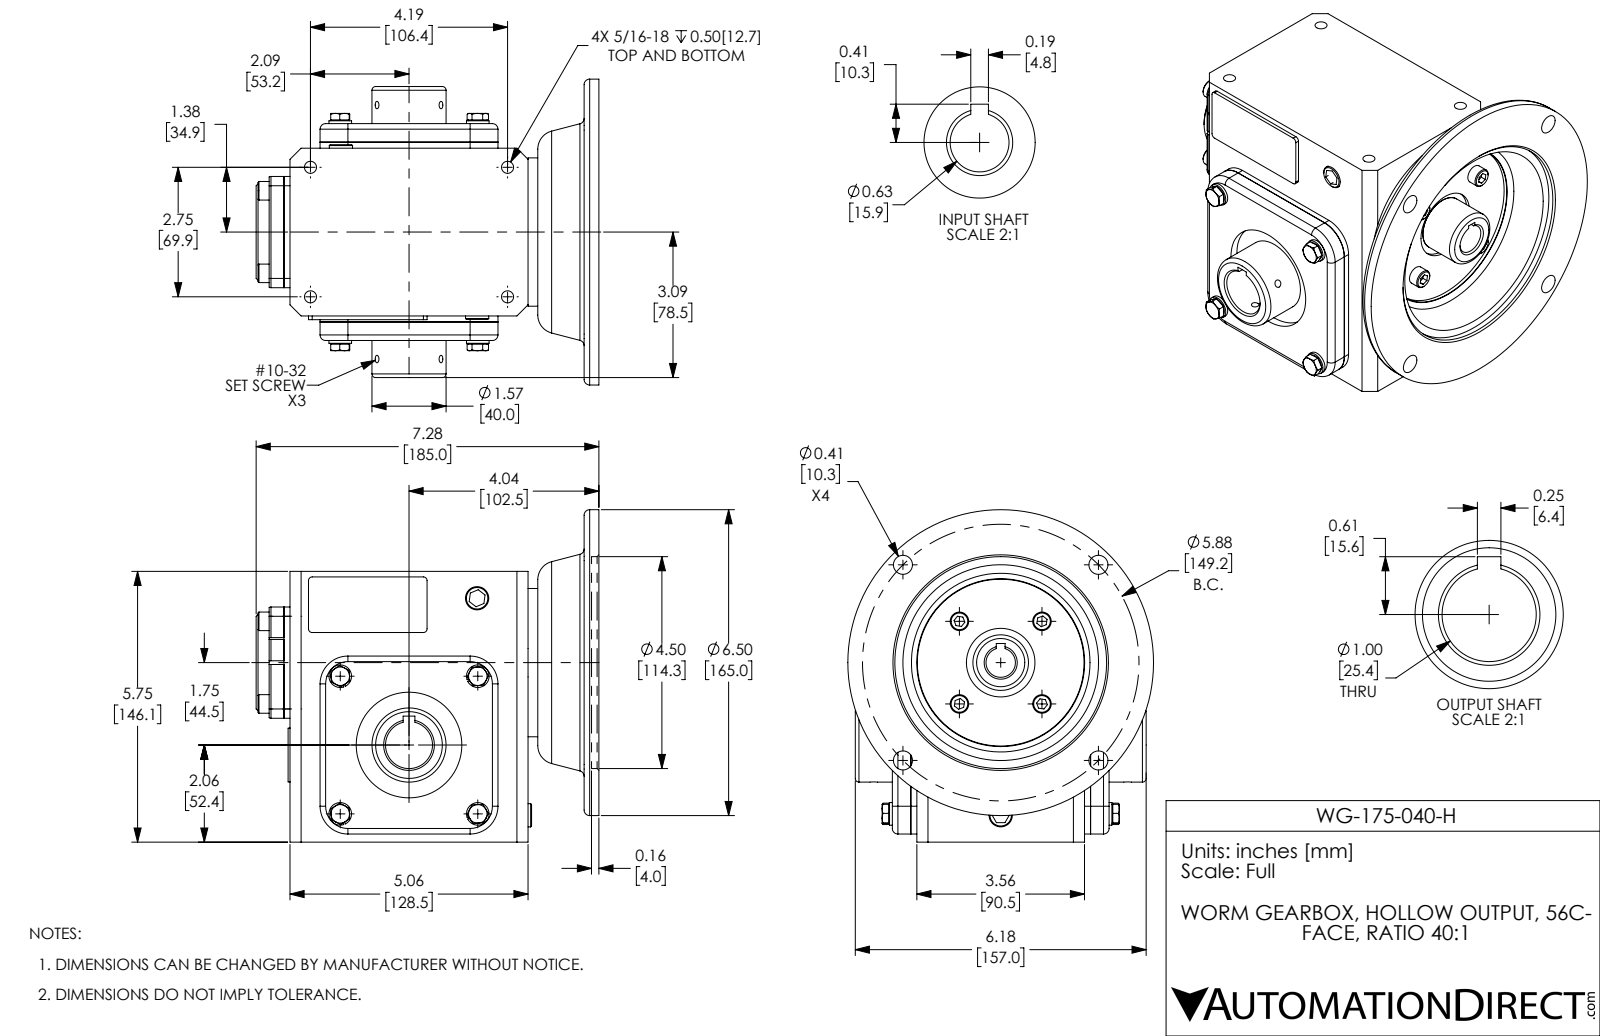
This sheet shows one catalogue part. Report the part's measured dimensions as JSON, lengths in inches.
{"part_name": "WG-175-040-H", "step_written_by": "SolidWorks 2015 (CONFIG_CONTROL_DESIGN)", "units": "inches", "bodies": {"solids": 44, "faces": 661, "planar": 339, "cylindrical": 194, "other": 128}, "overall_size": [7.283, 7.06, 6.496], "volume_in3": 131.1, "surface_area_in2": 382.7, "round_holes": [[0.159, 6], [0.257, 4], [0.406, 4], [0.591, 1], [0.625, 1], [1, 1], [1.457, 1], [1.575, 1], [2.244, 1], [3.543, 1], [4.5, 1]], "round_bosses_or_shafts": [[0.394, 8], [0.118, 5], [0.48, 4], [6.496, 1], [3.15, 1], [2.047, 1], [1.575, 1], [1.181, 1]], "partial_cylinders_radius": [[0.079, 8], [0.118, 8], [0.197, 4], [0.591, 4], [0.02, 2], [0.039, 2]], "face_to_face_distances": [0.128, 3.819, 3.691, 0.394, 0.522, 4.085, 4.213, 5.75, 0.315, 6.693], "hole_center_spacings": [2.476, 2.937, 4.154, 4.579, 5.394, 2.08, 2.75, 4.188]}
